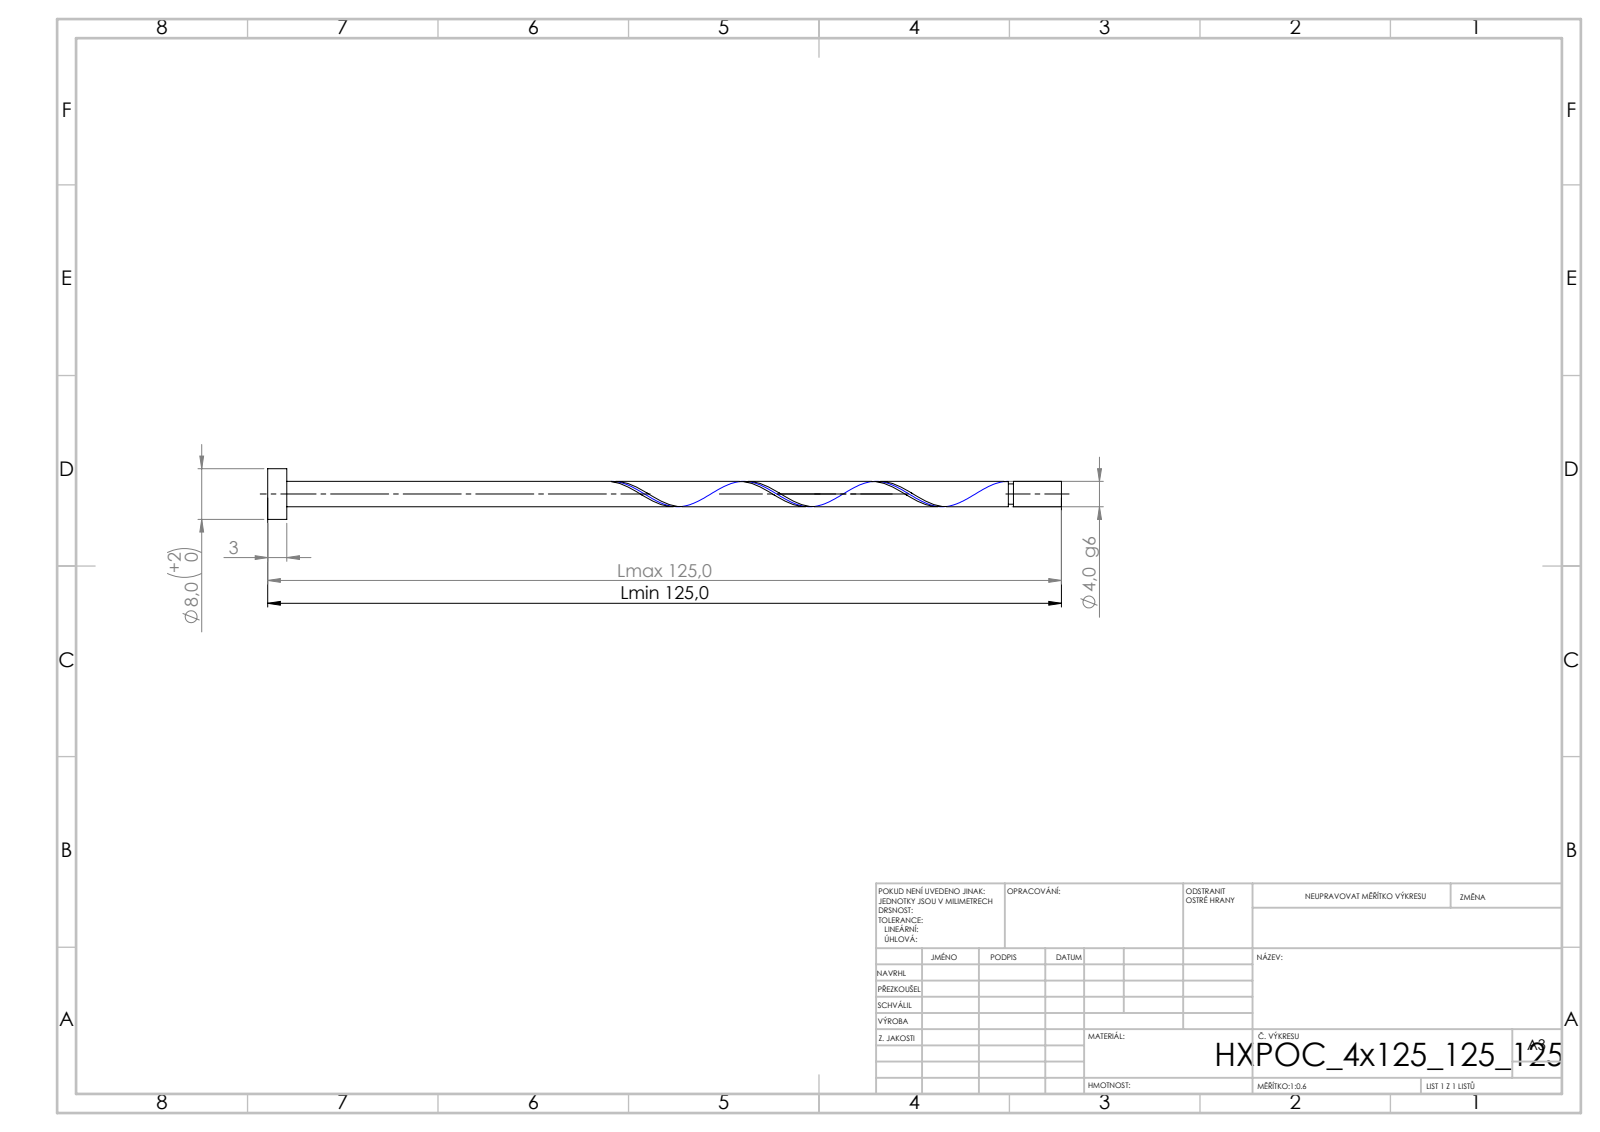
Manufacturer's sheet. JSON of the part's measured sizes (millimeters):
{"step_written_by": "SolidWorks 2019 (CONFIG_CONTROL_DESIGN)", "units": "millimeters", "bodies": {"solids": 1, "faces": 21, "planar": 6, "cylindrical": 14, "other": 1}, "overall_size": [125, 8, 8], "volume_mm3": 1665, "surface_area_mm2": 1745, "round_bosses_or_shafts": [[8, 1], [4, 1], [3.2, 1]], "face_to_face_distances": [3, 125, 122, 117.44, 114.44, 7.56, 116.64, 113.64, 0.8, 8.36]}
